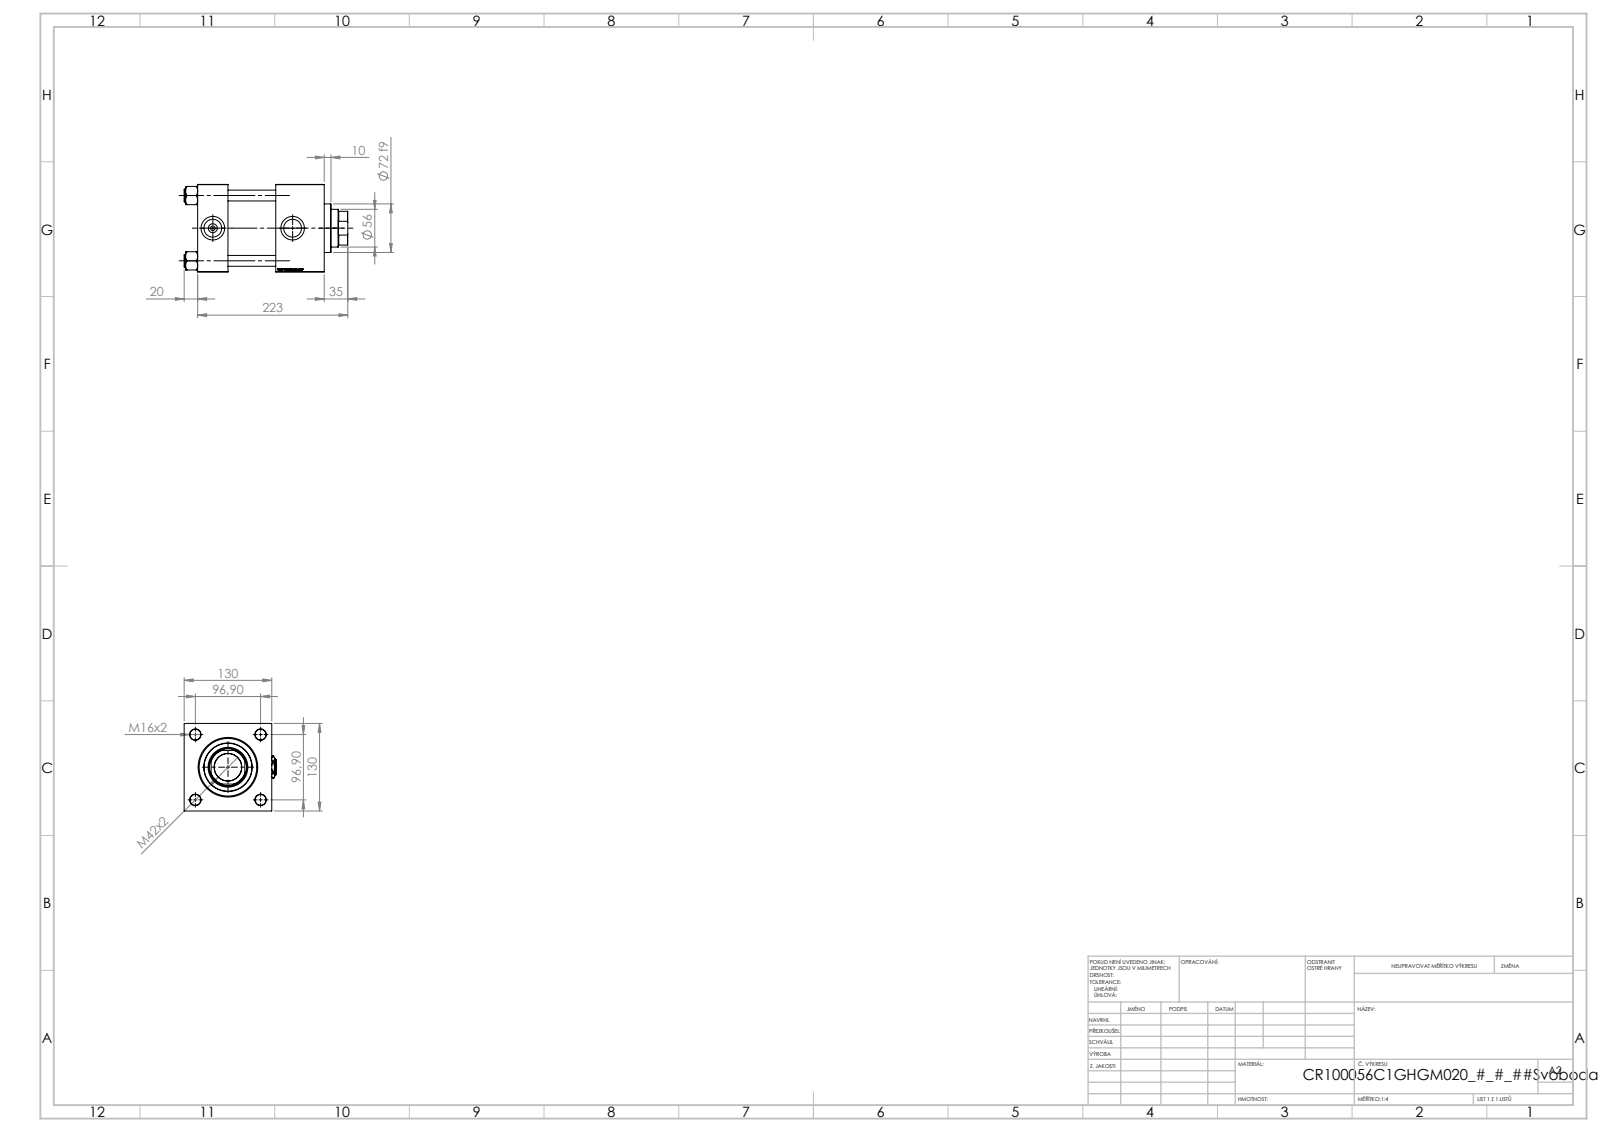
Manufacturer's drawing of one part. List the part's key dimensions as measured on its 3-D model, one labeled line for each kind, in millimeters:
Part name (STEP PRODUCT): V215CR_C_Body; NUT_M5_C; Zatka_pro_OIL_PORT; V215_VC_A (+2 more)
STEP written by: SolidWorks 2019 (CONFIG_CONTROL_DESIGN)
Units: millimetres
Bodies: 12 solids, 1243 faces (597 planar, 90 cylindrical, 556 other)
Overall size (bounding box): 243 × 137 × 130
Volume: 2 464 000 mm³ · Surface area: 336 624 mm²
Round holes (diameter × count): ⌀16 ×4, ⌀7 ×2, ⌀26.44 ×2, ⌀35 ×2, ⌀40.5 ×1, ⌀56 ×1, ⌀59 ×1, ⌀76 ×1, ⌀85.5 ×1, ⌀100 ×1
Round bosses / shafts (diameter × count): ⌀19 ×4, ⌀106 ×1, ⌀72 ×1
Partial cylindrical surfaces — rounded edges, fillets, slot ends (radius × count): R27 ×1
Main face-to-face distances: 130, 45, 188, 143, 116, 71, 72, 20, 51, 96
Hole centre spacings: 68.52, 96.9, 137.04, 118.5
